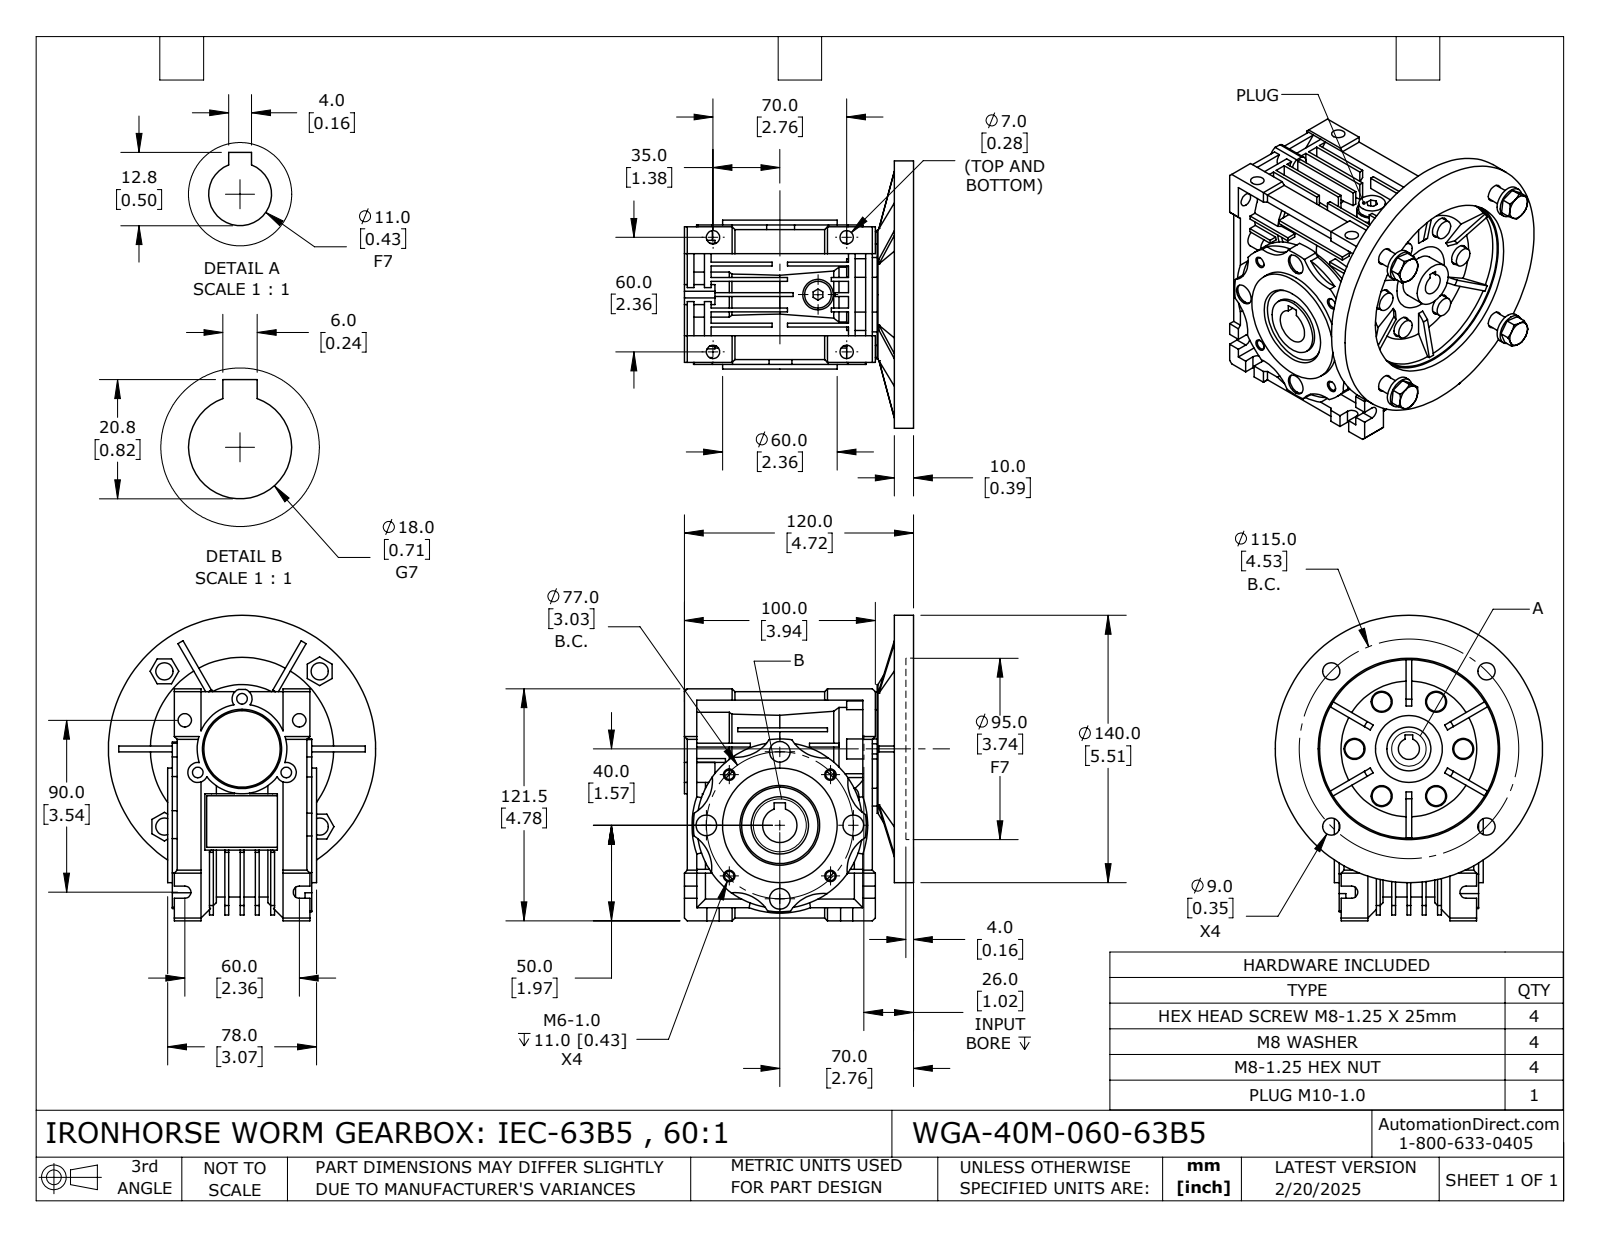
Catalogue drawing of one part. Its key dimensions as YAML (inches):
part_name: "WGA-40M-060-63B5"
step_written_by: "SolidWorks 2024 (CONFIG_CONTROL_DESIGN)"
units: inches
bodies: {solids: 18, faces: 1083, planar: 592, cylindrical: 298, other: 193}
overall_size: [6.299, 5.512, 5.432]
volume: 45.77
surface_area: 295.5
round_holes:
  - {diameter: 0.433, count: 7}
  - {diameter: 0.276, count: 6}
  - {diameter: 0.354, count: 5}
  - {diameter: 0.194, count: 4}
  - {diameter: 0.268, count: 4}
  - {diameter: 0.315, count: 4}
  - {diameter: 0.359, count: 4}
  - {diameter: 0.425, count: 4}
  - {diameter: 0.219, count: 3}
  - {diameter: 0.453, count: 1}
  - {diameter: 0.709, count: 1}
  - {diameter: 0.906, count: 1}
round_bosses_or_shafts:
  - {diameter: 0.394, count: 6}
  - {diameter: 0.63, count: 5}
  - {diameter: 5.512, count: 1}
  - {diameter: 2.953, count: 1}
  - {diameter: 2.657, count: 1}
  - {diameter: 2.362, count: 1}
  - {diameter: 2.126, count: 1}
  - {diameter: 1.85, count: 1}
partial_cylinders:
  - {radius: 0.787, count: 8}
  - {radius: 0.126, count: 6}
  - {radius: 0.206, count: 6}
  - {radius: 0.207, count: 3}
  - {radius: 1.713, count: 1}
  - {radius: 1.716, count: 1}
  - {radius: 1.781, count: 1}
  - {radius: 1.811, count: 1}
face_to_face_distances: [0.394, 0.315, 0.236, 0.079, 0.197, 0.059, 0.63, 0.945, 0.551, 0.098]
hole_center_spacings: [1.122, 1.146, 2.765, 1.943, 1.215, 1.32, 1.476, 1.516]
